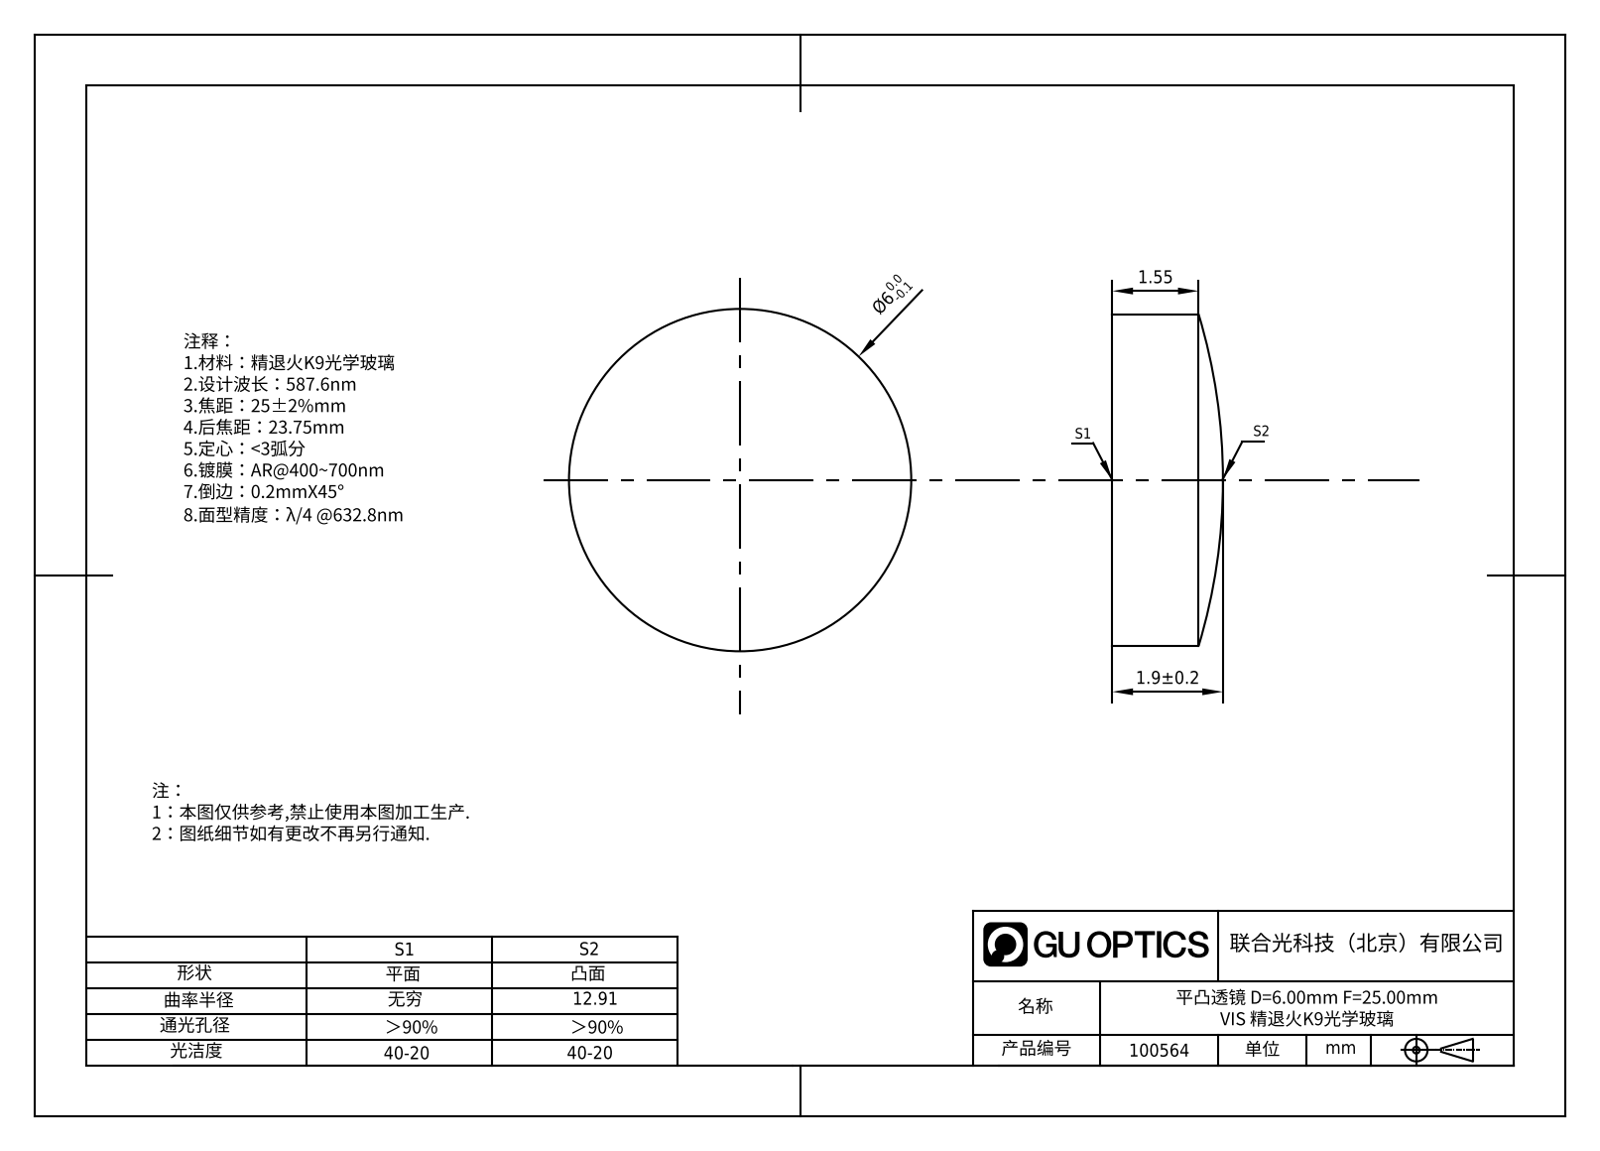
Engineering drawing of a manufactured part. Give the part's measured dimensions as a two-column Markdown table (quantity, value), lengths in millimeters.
| quantity | value |
| --- | --- |
| part name | 100564 |
| STEP written by | SolidWorks 2020 (CONFIG_CONTROL_DESIGN) |
| units | millimeters |
| bodies | 1 solid, 5 faces (1 planar, 2 cylindrical, 2 other) |
| overall size | 6 × 6 × 1.9 |
| volume | 49 mm³ |
| surface area | 86 mm² |
| round bosses / shafts (diameter × count) | 6 × 1 |
